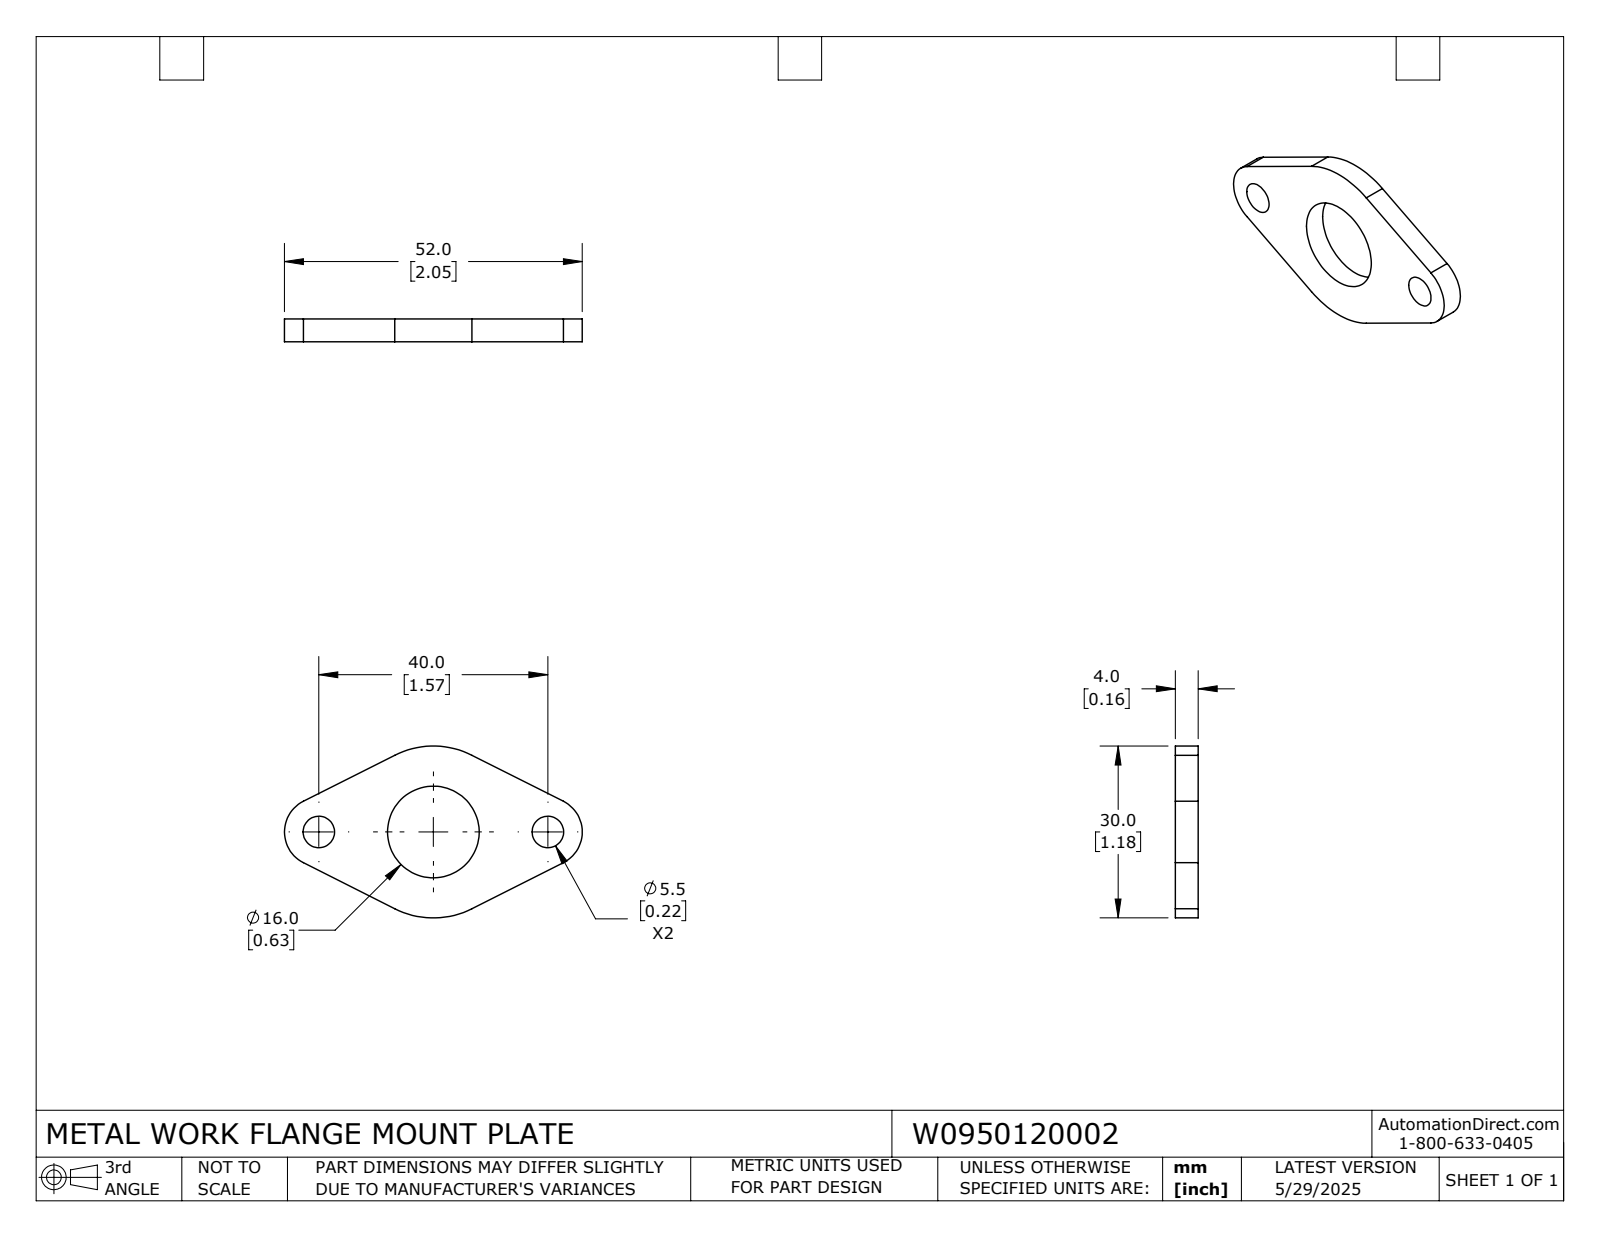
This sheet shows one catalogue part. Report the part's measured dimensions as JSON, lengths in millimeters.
{"part_name": "W0950120002", "step_written_by": "SolidWorks 2024 (CONFIG_CONTROL_DESIGN)", "units": "millimeters", "bodies": {"solids": 1, "faces": 17, "planar": 6, "cylindrical": 11, "other": 0}, "overall_size": [52, 30, 4], "volume_mm3": 3160, "surface_area_mm2": 2425, "round_holes": [[5.5, 2], [16, 1]], "partial_cylinders_radius": [[6, 2], [15, 1]], "face_to_face_distances": [4, 30], "hole_center_spacings": [20, 40]}
